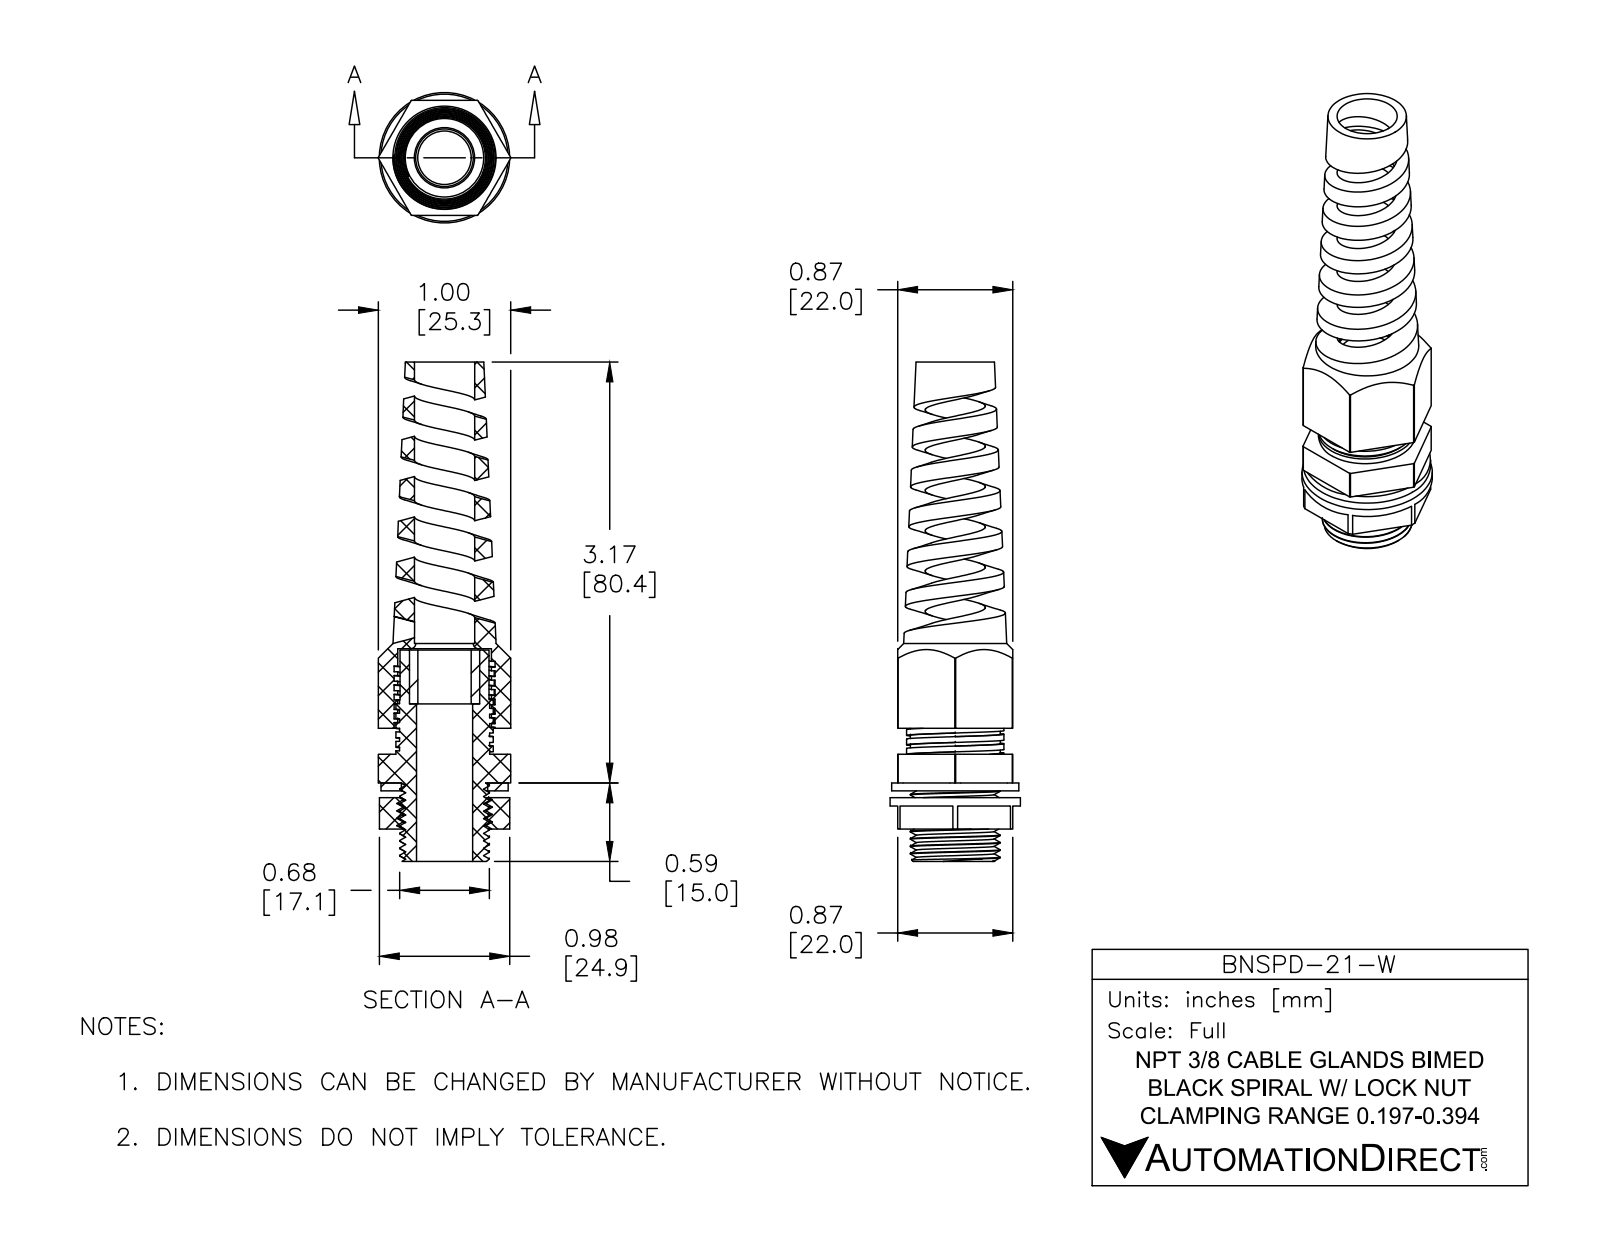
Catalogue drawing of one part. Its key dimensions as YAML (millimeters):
part_name: "BNSPAX-21-W"
step_written_by: "SolidWorks 2015 (CONFIG_CONTROL_DESIGN)"
units: millimeters
bodies: {solids: 5, faces: 242, planar: 104, cylindrical: 104, other: 34}
overall_size: [95.43, 25.3, 24.9]
volume: 14497
surface_area: 16500
round_holes:
  - {diameter: 10.2, count: 1}
  - {diameter: 10.72, count: 1}
  - {diameter: 11.5, count: 1}
  - {diameter: 13.4, count: 1}
  - {diameter: 16.02, count: 1}
  - {diameter: 16.5, count: 1}
  - {diameter: 17.9, count: 1}
round_bosses_or_shafts:
  - {diameter: 24.9, count: 1}
  - {diameter: 24.3, count: 1}
  - {diameter: 18.6, count: 1}
  - {diameter: 17.14, count: 1}
  - {diameter: 17, count: 1}
partial_cylinders:
  - {radius: 12.65, count: 1}
face_to_face_distances: [22, 7, 1, 2.5, 1.5, 6, 8.5, 9.6, 0.5, 14]
